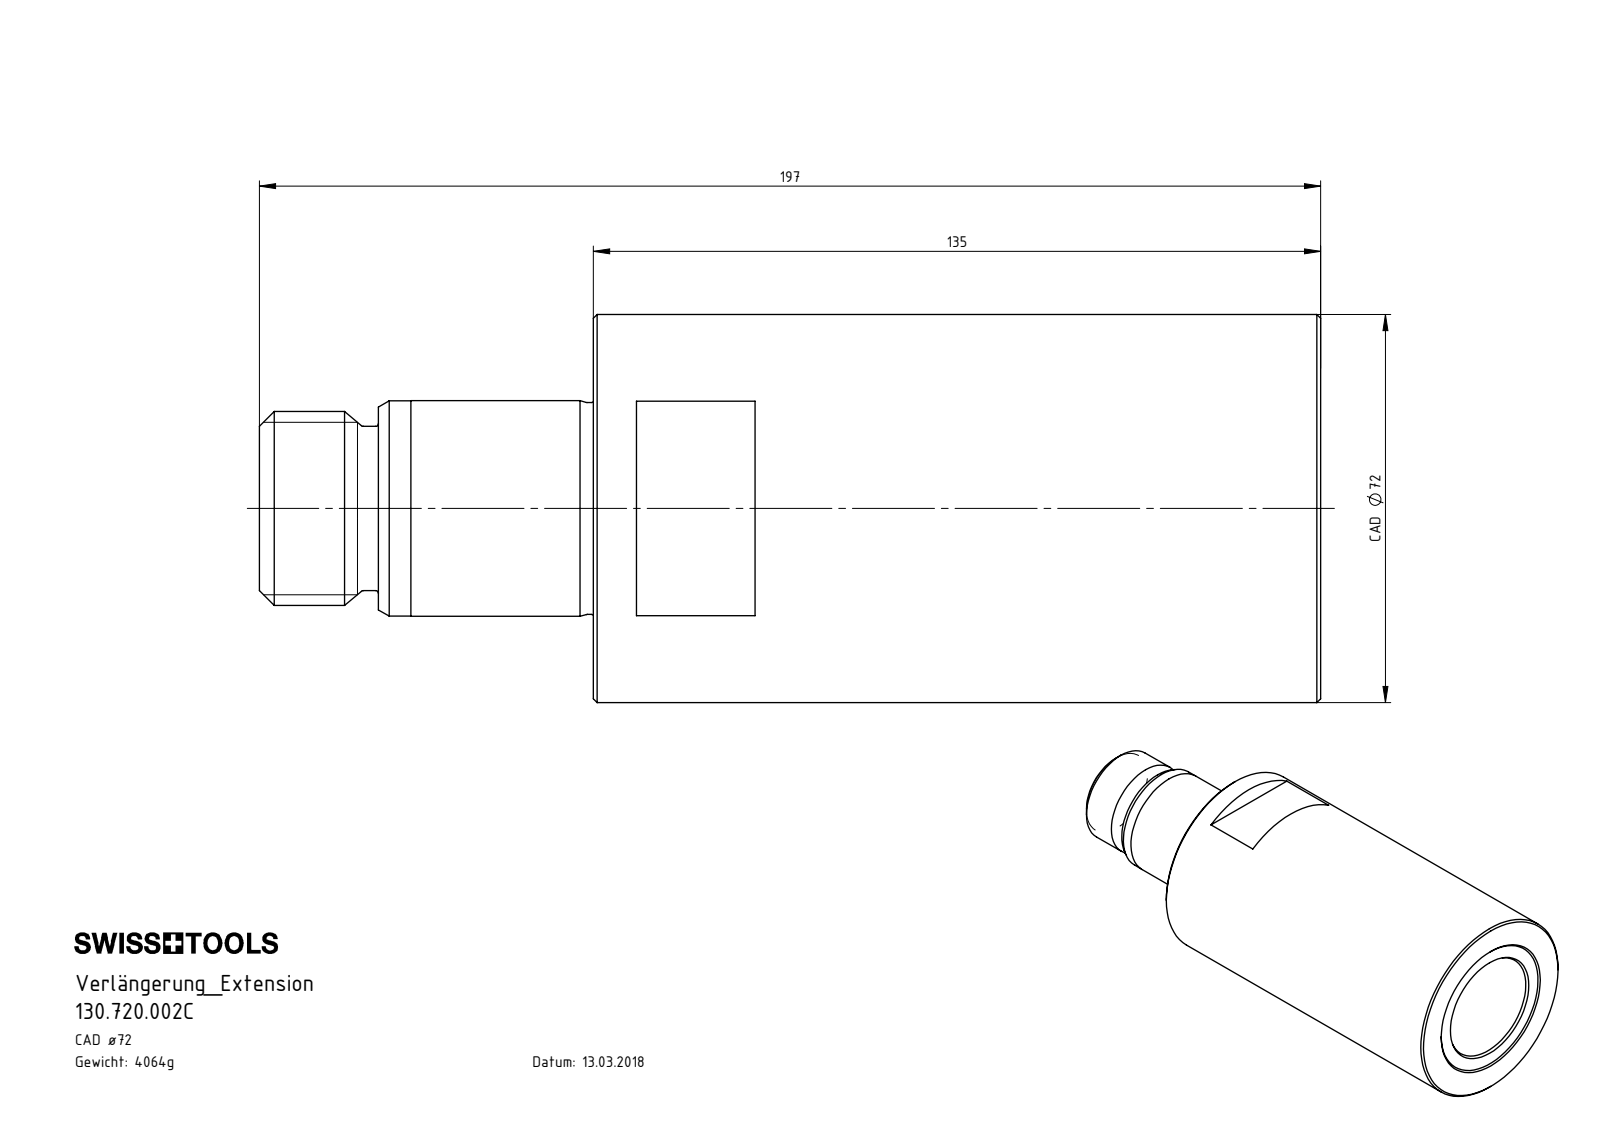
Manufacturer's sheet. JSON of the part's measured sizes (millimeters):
{"part_name": "130.720.002C", "step_written_by": "SolidWorks 2017 (CONFIG_CONTROL_DESIGN)", "units": "millimeters", "bodies": {"solids": 1, "faces": 71, "planar": 13, "cylindrical": 20, "other": 38}, "overall_size": [197, 72, 72], "volume_mm3": 517696, "surface_area_mm2": 58690, "round_holes": [[8.5, 1], [32, 1], [40, 1], [40.6, 1]], "round_bosses_or_shafts": [[72, 1], [39.95, 1], [39.3, 1], [36, 1], [30.5, 1]], "face_to_face_distances": [135, 60, 134.4, 0.6, 62, 196.4, 197, 22.1, 39.9, 174.3]}
